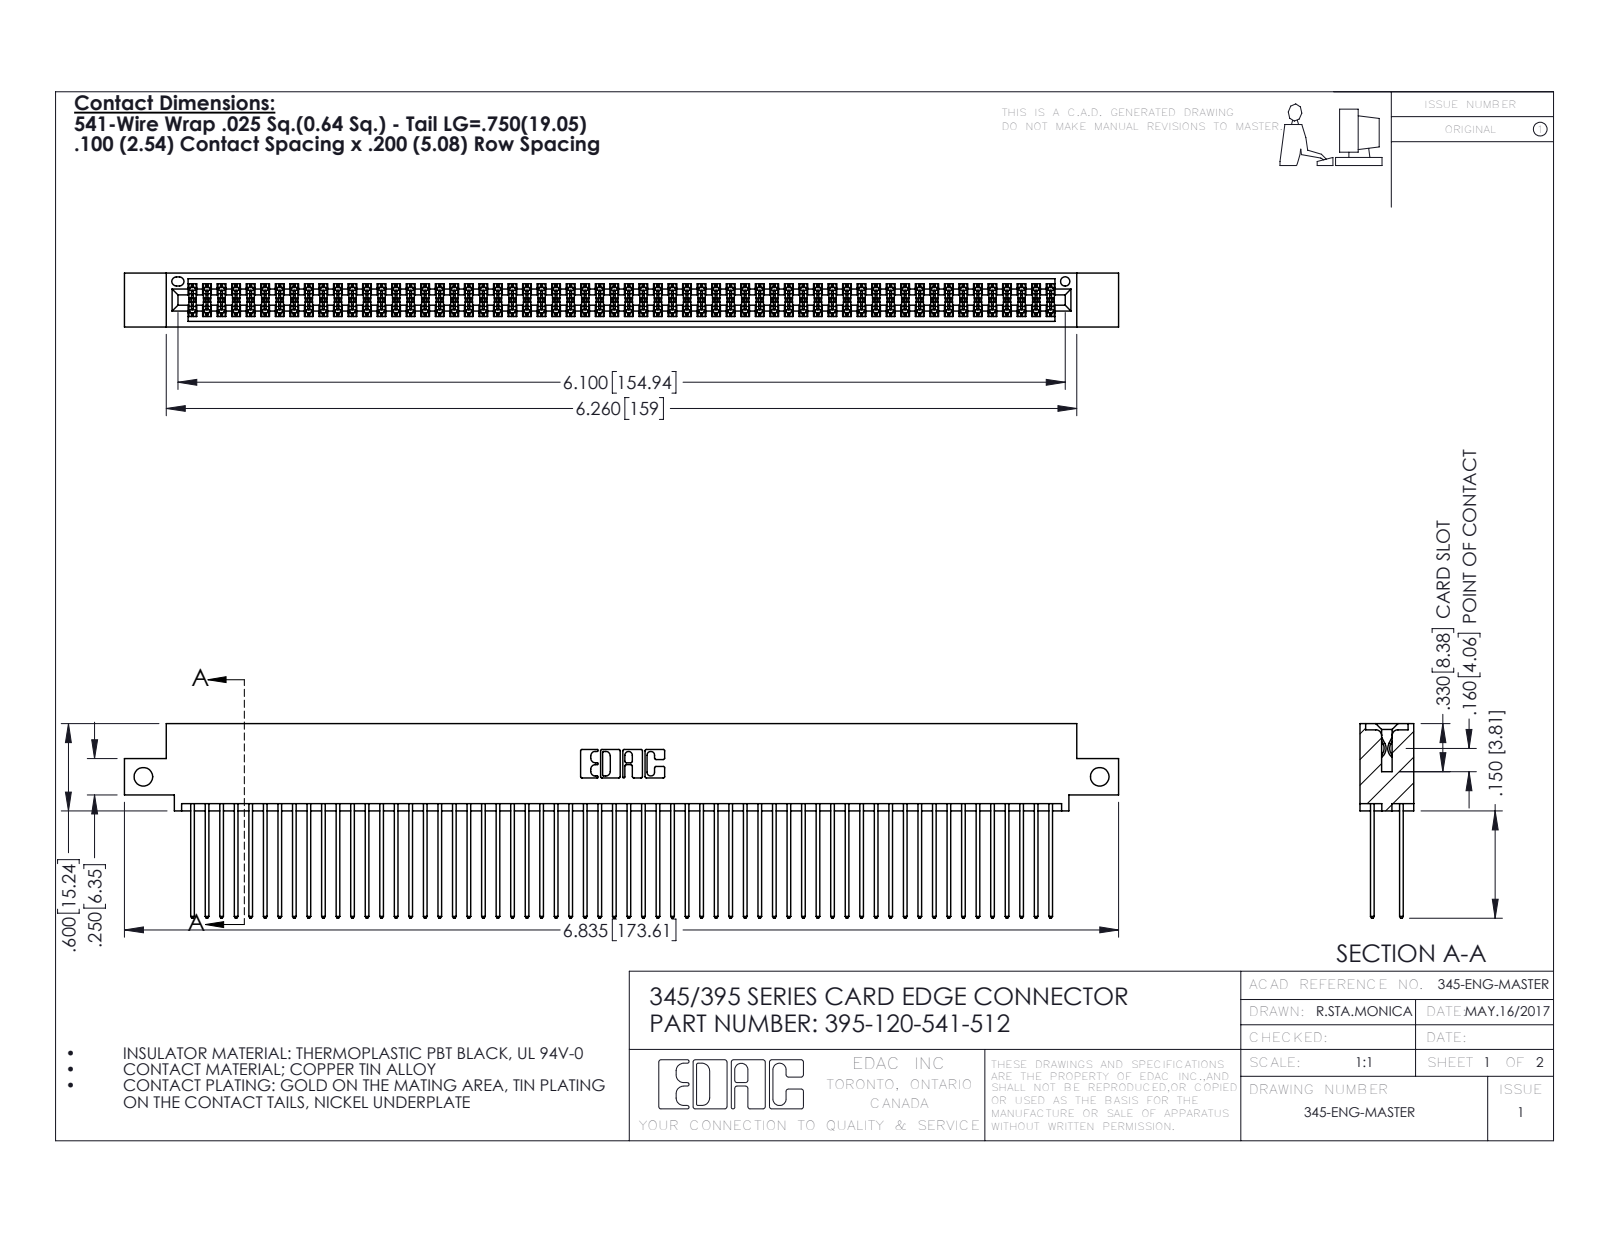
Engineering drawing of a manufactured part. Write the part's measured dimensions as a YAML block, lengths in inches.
part_name: "395-120-541-512; 345-292-001_345-293-141; 345 Part_0.110 Offset - Side Mount"
step_written_by: "SolidWorks 2016 (CONFIG_CONTROL_DESIGN)"
units: inches
bodies: {solids: 121, faces: 6130, planar: 4044, cylindrical: 2086, other: 0}
overall_size: [6.835, 1.337, 0.37]
volume: 1.072
surface_area: 45.72
round_holes:
  - {diameter: 0.128, count: 2}
  - {diameter: 0.064, count: 1}
partial_cylinders:
  - {radius: 0.006, count: 180}
  - {radius: 0.01, count: 120}
  - {radius: 0.01, count: 22}
  - {radius: 0.007, count: 6}
  - {radius: 0.031, count: 6}
  - {radius: 0.026, count: 3}
  - {radius: 0.014, count: 2}
  - {radius: 0.019, count: 2}
face_to_face_distances: [0.072, 0.298, 0.2, 0.098, 0.272, 0.025, 0.225, 0.37, 0.175, 0.149]
hole_center_spacings: [6.575]
